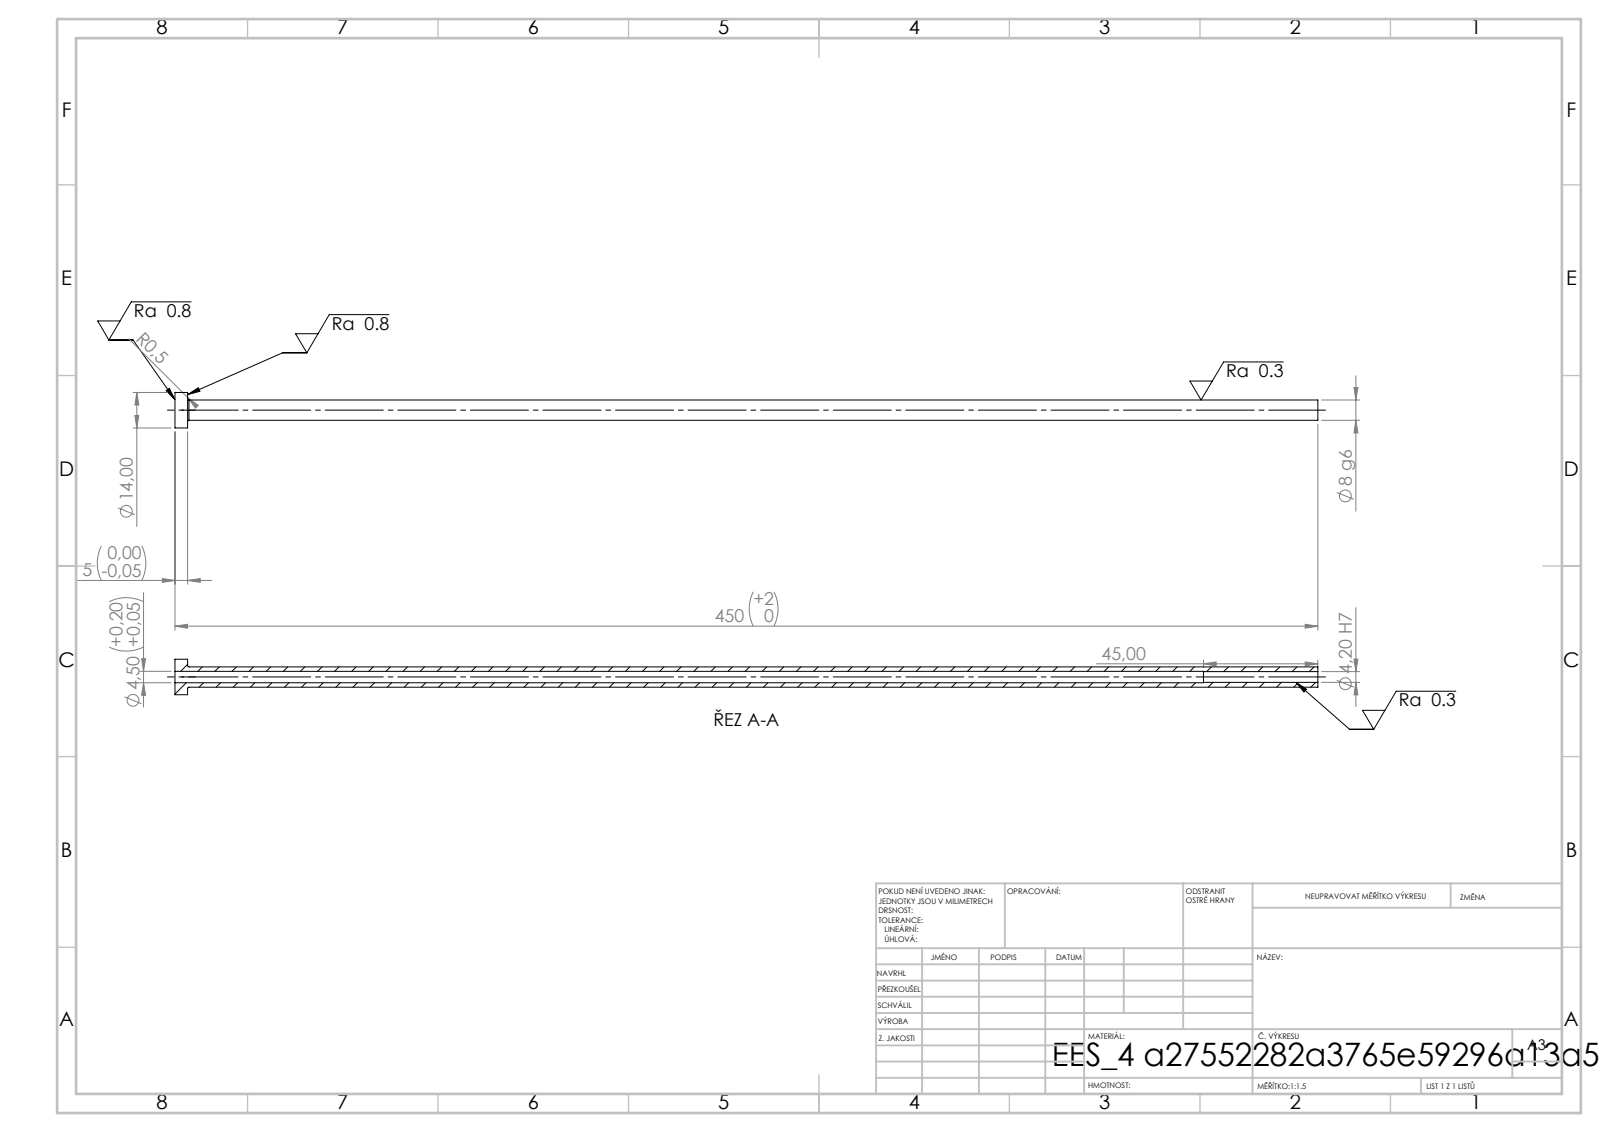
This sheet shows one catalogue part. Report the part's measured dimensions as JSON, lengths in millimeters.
{"step_written_by": "SolidWorks 2019 (CONFIG_CONTROL_DESIGN)", "units": "millimeters", "bodies": {"solids": 1, "faces": 14, "planar": 4, "cylindrical": 8, "other": 2}, "overall_size": [450, 14, 14], "volume_mm3": 16075, "surface_area_mm2": 17998, "round_holes": [[4.2, 1], [4.5, 1]], "round_bosses_or_shafts": [[14, 1], [8, 1]], "face_to_face_distances": [5, 450, 445, 405, 400, 45]}
